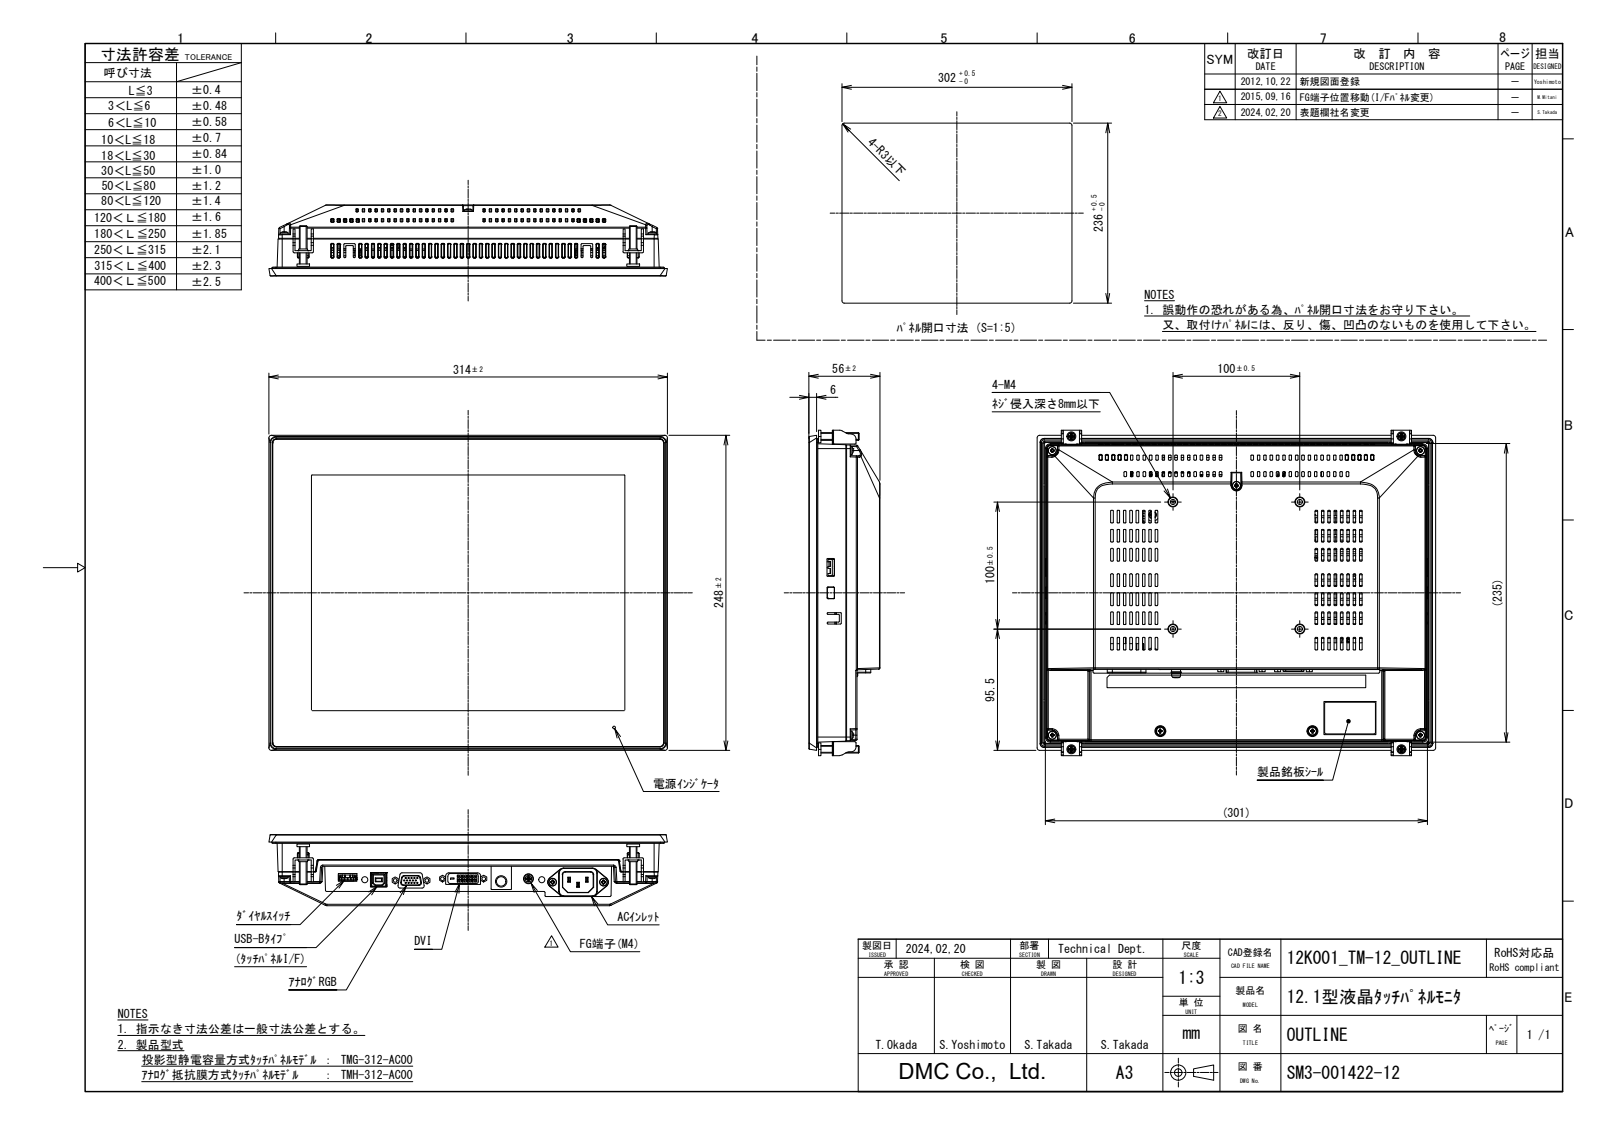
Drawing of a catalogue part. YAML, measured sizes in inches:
part_name: "HP_TMG(H)-312-AC00"
step_written_by: "Autodesk Inventor 2017 (CONFIG_CONTROL_DESIGN)"
units: inches
bodies: {solids: 5, faces: 7136, planar: 3824, cylindrical: 1495, other: 1817}
overall_size: [12.362, 10.09, 2.205]
volume: 39.34
surface_area: 1122
round_holes:
  - {diameter: 0.138, count: 122}
  - {diameter: 0.118, count: 36}
  - {diameter: 0.315, count: 22}
  - {diameter: 0.039, count: 18}
  - {diameter: 0.157, count: 14}
  - {diameter: 0.126, count: 7}
  - {diameter: 0.177, count: 6}
  - {diameter: 0.189, count: 5}
  - {diameter: 0.098, count: 4}
  - {diameter: 0.354, count: 4}
  - {diameter: 0.394, count: 4}
  - {diameter: 0.102, count: 2}
round_bosses_or_shafts:
  - {diameter: 0.242, count: 16}
  - {diameter: 0.118, count: 9}
  - {diameter: 0.244, count: 8}
  - {diameter: 0.157, count: 6}
  - {diameter: 0.142, count: 6}
  - {diameter: 0.281, count: 5}
  - {diameter: 0.276, count: 5}
  - {diameter: 0.394, count: 4}
partial_cylinders:
  - {radius: 0.02, count: 267}
  - {radius: 0.012, count: 140}
  - {radius: 0.039, count: 134}
  - {radius: 0.051, count: 18}
  - {radius: 0.004, count: 17}
  - {radius: 0.079, count: 16}
  - {radius: 0.118, count: 14}
  - {radius: 0.043, count: 13}
face_to_face_distances: [0.039, 0.748, 0.791, 0.043, 0.831, 0.118, 0.787, 1.091, 0.197, 1.051]
hole_center_spacings: [0.09, 0.156, 0.197, 0.09, 0.18, 0.18, 0.238, 0.156]
